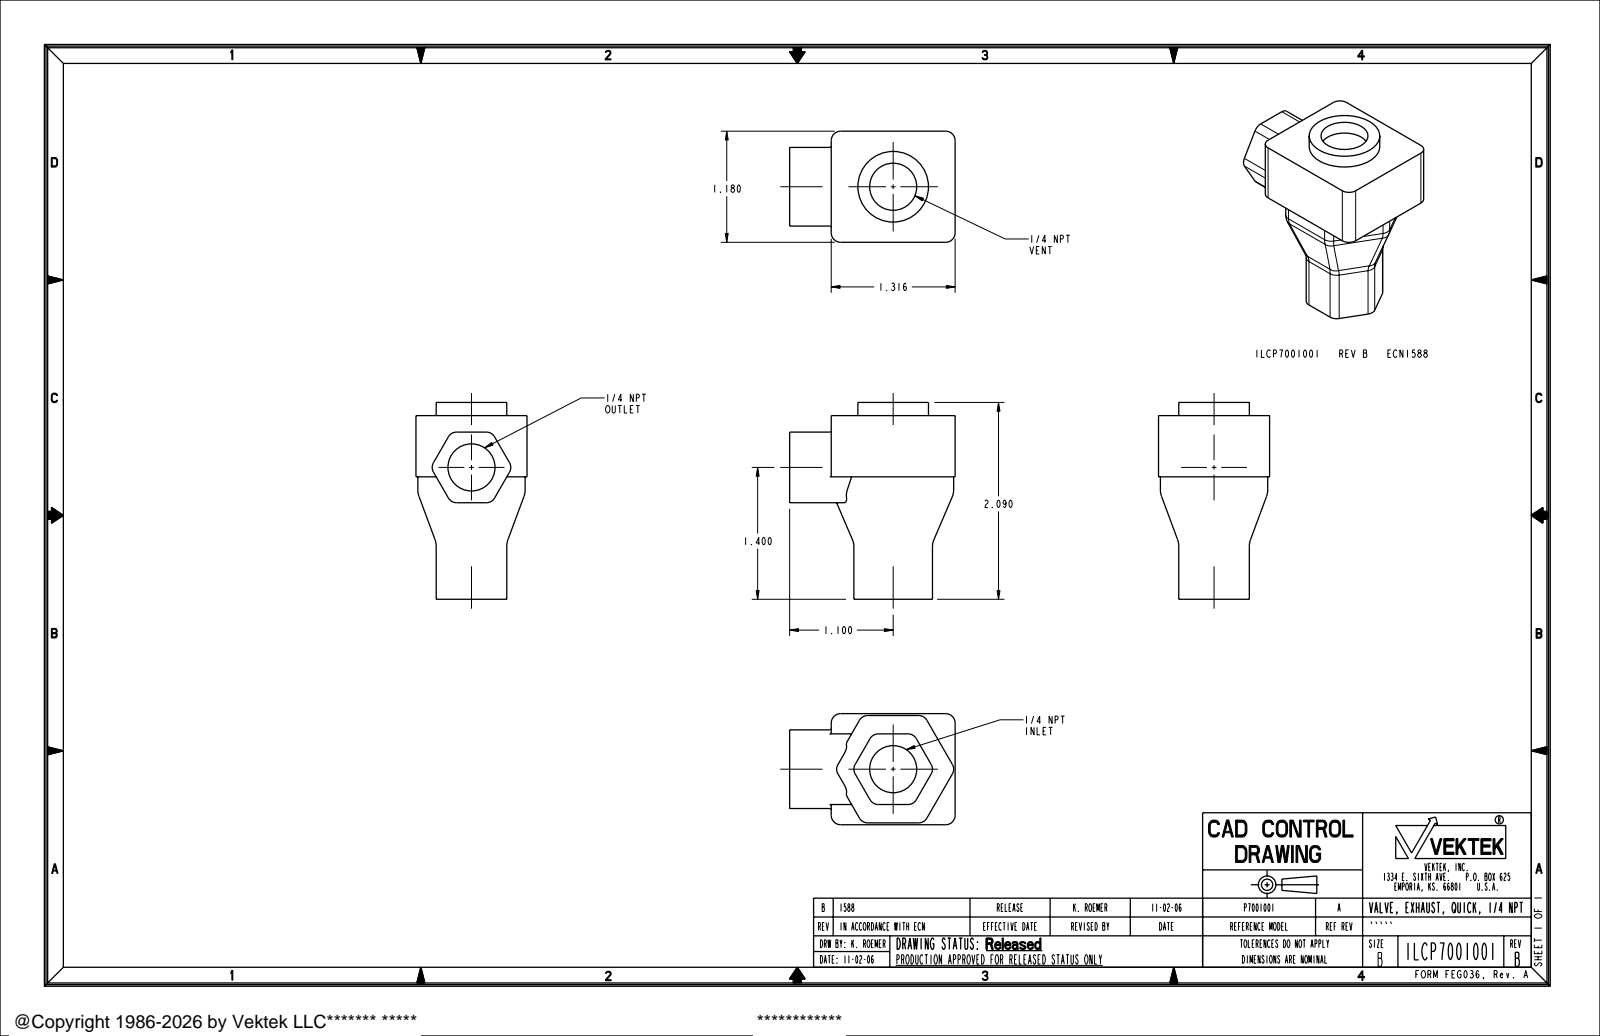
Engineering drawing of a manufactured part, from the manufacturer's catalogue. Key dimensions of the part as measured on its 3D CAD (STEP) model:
Part name (STEP PRODUCT): ILCP7001001
STEP written by: PRO/ENGINEER BY PARAMETRIC TECHNOLOGY CORPORATION, 2005180 (AUTOMOTIVE_DESIGN_CC2)
Units: inches
Bodies: 1 solid, 103 faces (36 planar, 52 cylindrical, 15 other)
Overall size (bounding box): 2.09 × 1.758 × 1.18
Volume: 2.066 in³ · Surface area: 12.08 in²
Round holes (diameter × count): ⌀0.5 ×2
Round bosses / shafts (diameter × count): ⌀0.75 ×1
Partial cylindrical surfaces — rounded edges, fillets, slot ends (radius × count): R0.1 ×27, R0.2 ×12, R0.015 ×5
Main face-to-face distances: 1.18, 0.75, 0.25, 0.195, 0.945, 0.215, 0.965, 0.65, 1.317, 1.758
